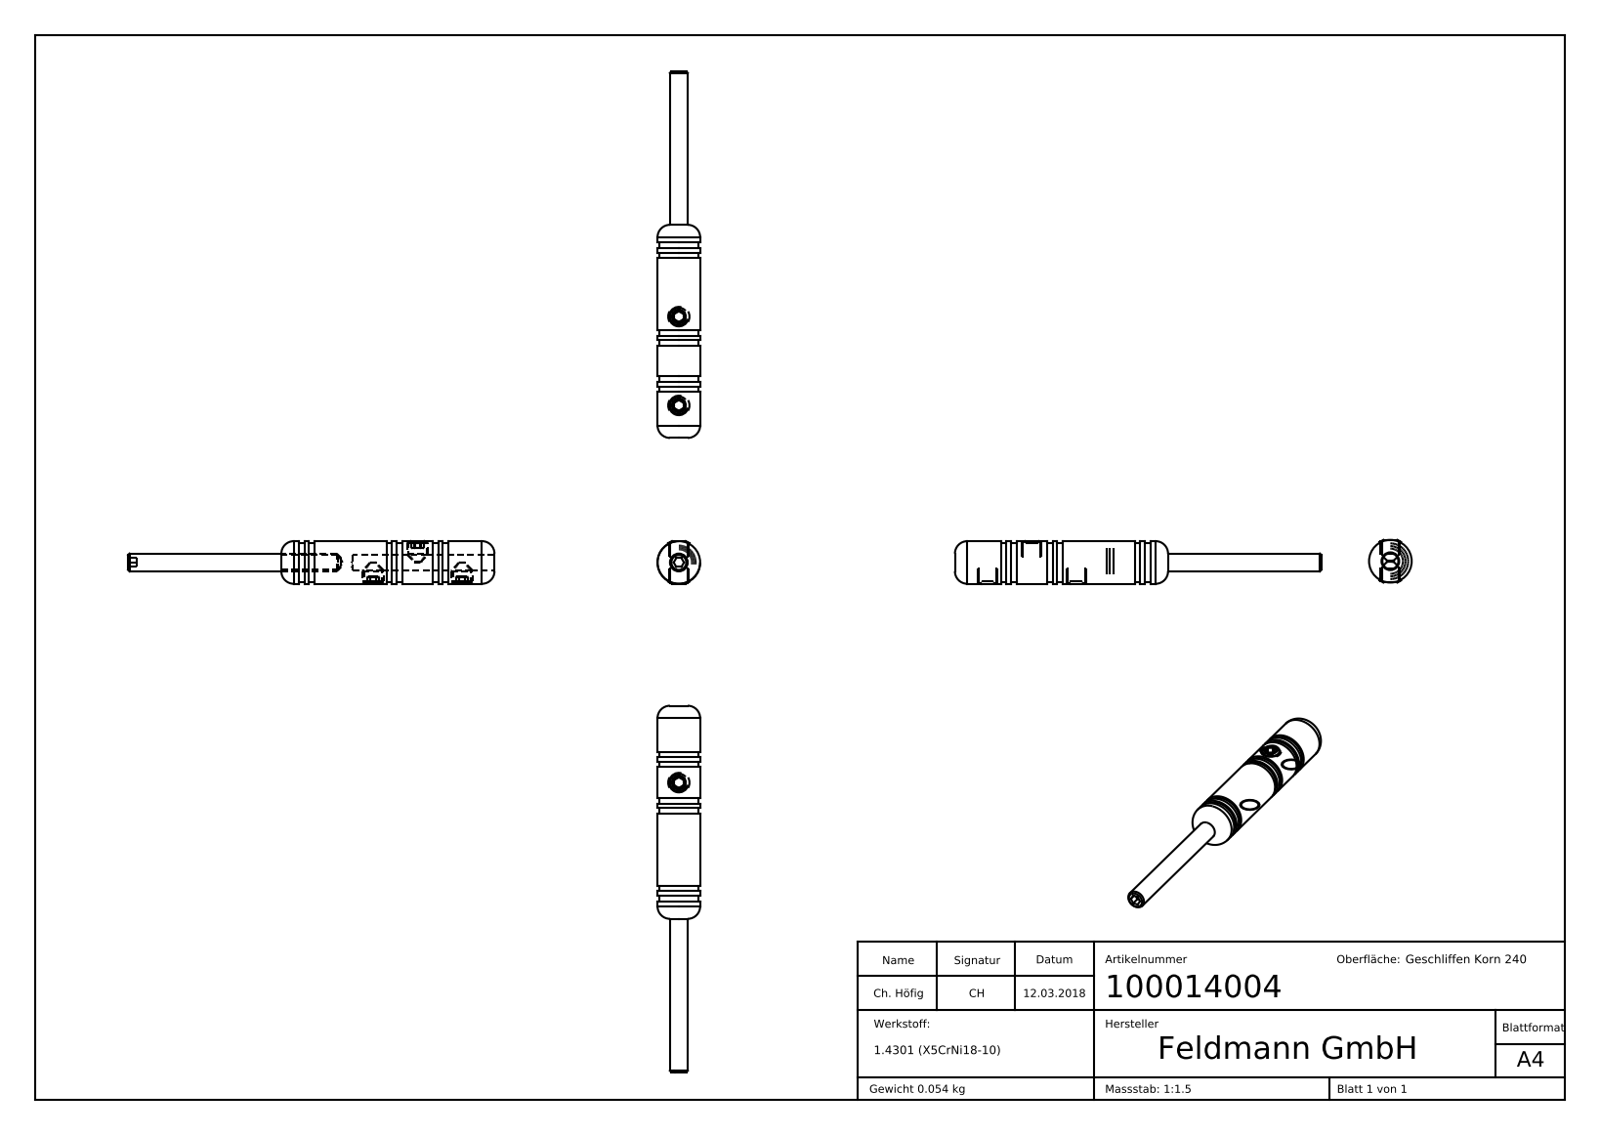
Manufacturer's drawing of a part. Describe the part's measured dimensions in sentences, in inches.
The part is named "DIN914_DIN 914 M6x6; 10001X00X Teil 1_100014004 Teil1; DIN913_DIN913 M5x60; 100014004". Its 3-D file was written by "SolidWorks 2015 (CONFIG_CONTROL_DESIGN)". It is 5 solids with 437 faces: 176 planar, 98 cylindrical and 163 other. Overall it measures 4.061 by 0.472 by 0.472 inches. Its volume is 0.417 cubic inches and its surface area 7.502 square inches. Round holes: 3 of diameter 0.197, 1 of diameter 0.165, 1 of diameter 0.177. Round bosses or shafts: 3 of diameter 0.236, 1 of diameter 0.472, 1 of diameter 0.433, 1 of diameter 0.197. Partial cylindrical surfaces (rounded edges, fillets, slot ends): 50 of radius 0.008. The main face-to-face distances are 0.059, 0.11, 0.512, 0.972, 1.484, 0.051, 0.169, 0.571, 0.622, 1.083. The hole center spacings are 0.492, 0.984.
